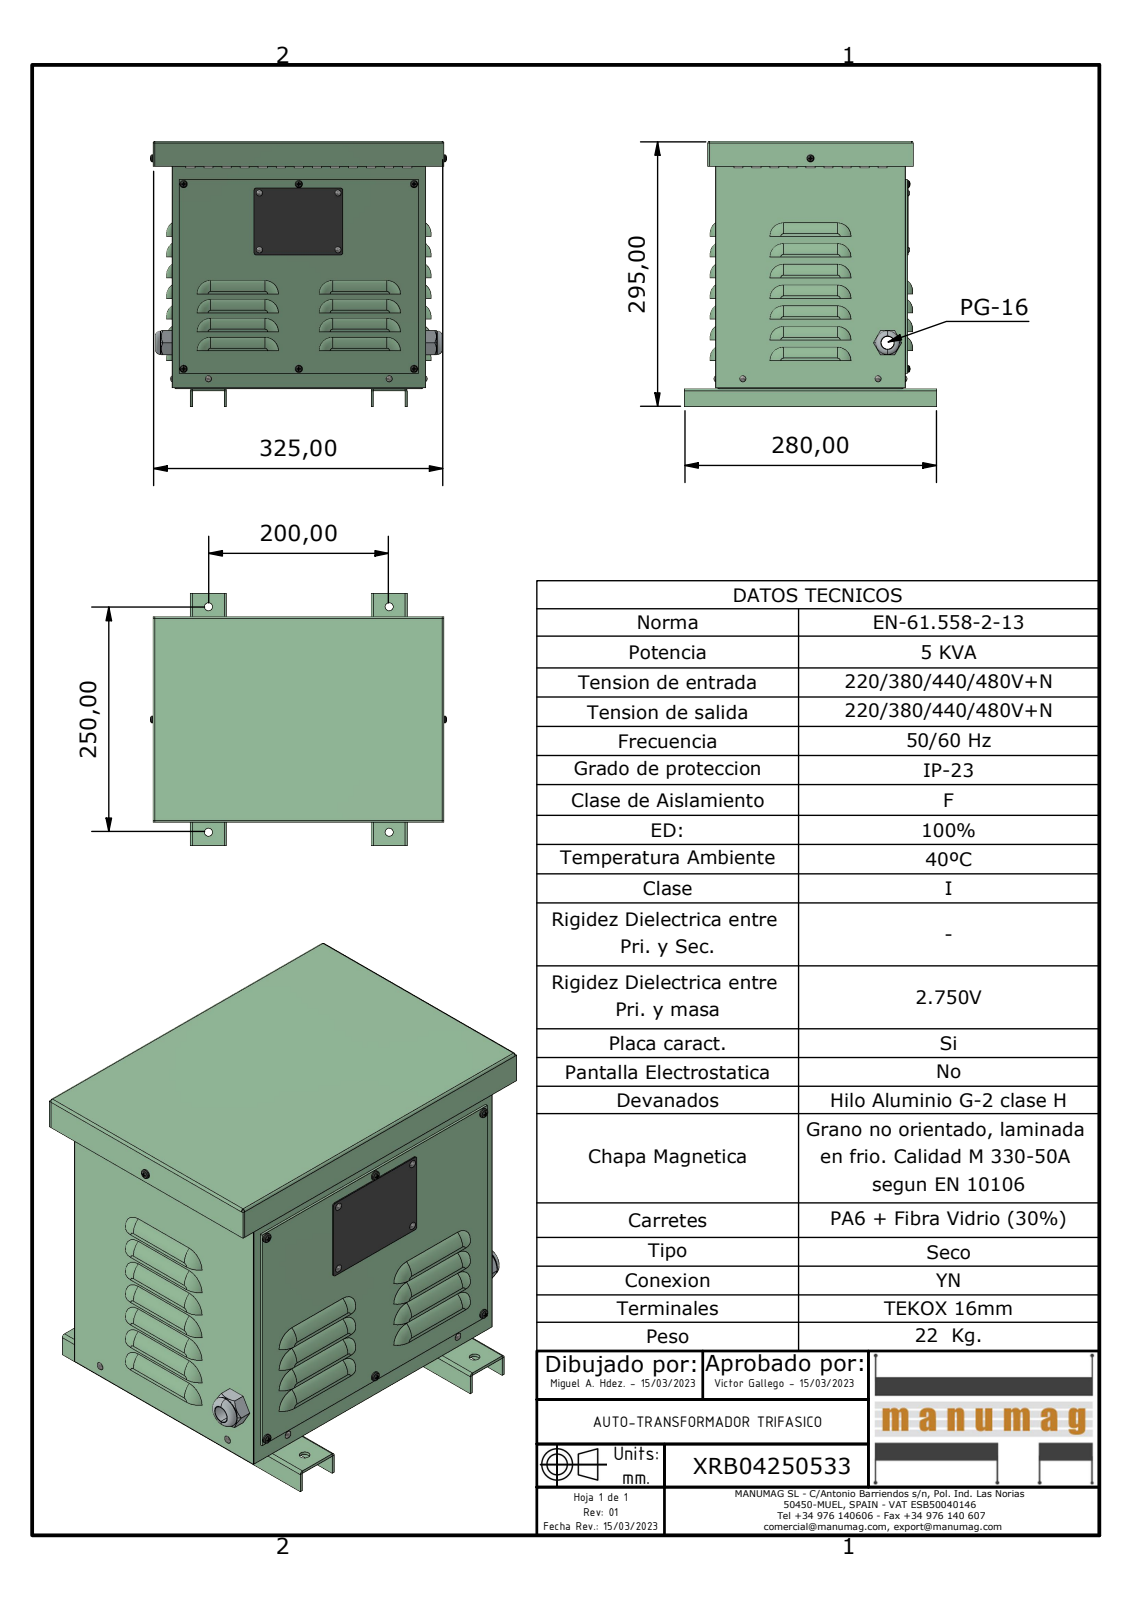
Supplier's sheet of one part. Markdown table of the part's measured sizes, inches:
| quantity | value |
| --- | --- |
| part name | XRB04250533; JE003 - JE004 - JE005 EXPORT BASE; JE003 - JE004 - JE005 EXPORT PATA; JE003 - JE004 - JE005 EXPORT CUERPO (+6 more) |
| STEP written by | Autodesk Inventor 2023 (AUTOMOTIVE_DESIGN) |
| units | inches |
| bodies | 29 solids, 1436 faces (841 planar, 283 cylindrical, 312 other) |
| overall size | 12.919 × 11.594 × 11.024 |
| volume | 50.51 in³ |
| surface area | 1 645 in² |
| round holes (diameter × count) | 0.189 × 13, 0.118 × 12, 0.354 × 6, 0.15 × 5, 0.157 × 4, 0.551 × 1, 0.945 × 1 |
| round bosses / shafts (diameter × count) | 0.126 × 8, 0.157 × 7, 0.143 × 7, 1.024 × 1, 0.906 × 1, 0.886 × 1 |
| partial cylindrical surfaces (radius × count) | 0.551 × 44, 0.157 × 25, 0.591 × 25, 0.02 × 9, 0.079 × 8, 0.177 × 8, 0.059 × 6, 0.059 × 4 |
| main face-to-face distances | 0.02, 0.079, 8.287, 11.043, 0.098, 0.059, 10.807, 10.728, 8.307, 8.386 |
| hole center spacings | 5.02, 7.874, 9.505, 8.071, 1.166, 1.757, 1.85, 2.48 |
